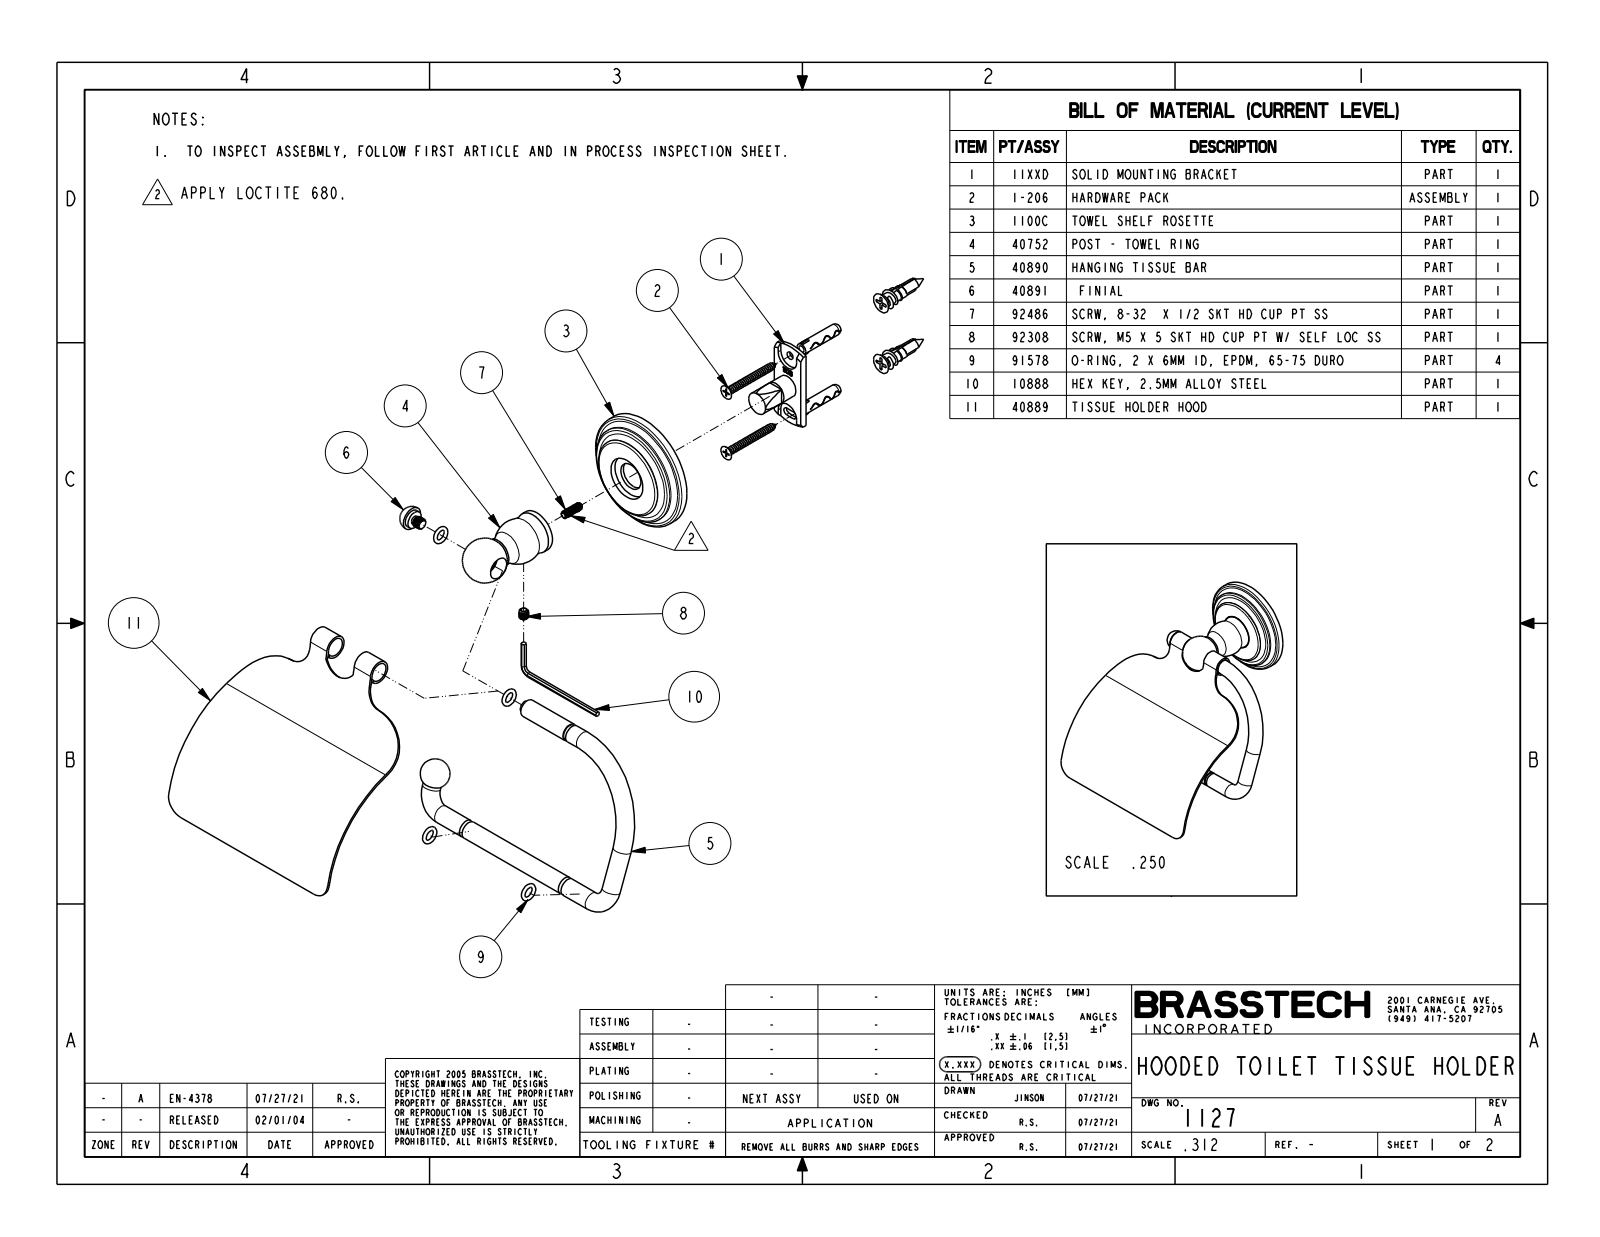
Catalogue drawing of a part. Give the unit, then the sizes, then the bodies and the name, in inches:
Units: inches
Overall size (bounding box): 5.878 × 4.993 × 4.958
Round bosses / shafts (diameter × count): ⌀0.394 ×4, ⌀2.56 ×1, ⌀2.182 ×1, ⌀1.748 ×1, ⌀0.514 ×1
Partial cylindrical surfaces — rounded edges, fillets, slot ends (radius × count): R0.394 ×4, R1.085 ×2, R0.207 ×1, R0.512 ×1, R1.5 ×1, R1.55 ×1, R2.5 ×1, R2.55 ×1
Main face-to-face distances: 0.512, 0.362, 0.15, 0.189, 0.173, 0.323, 1.479, 3.27, 4.75, 1.791
Volume: 5.583 in³ · Surface area: 75.18 in²
Bodies: 1 solid, 93 faces (16 planar, 35 cylindrical, 42 other)
Part name (STEP PRODUCT): 1127
STEP written by: CREO PARAMETRIC BY PTC INC, 2018400 (CONFIG_CONTROL_DESIGN)
